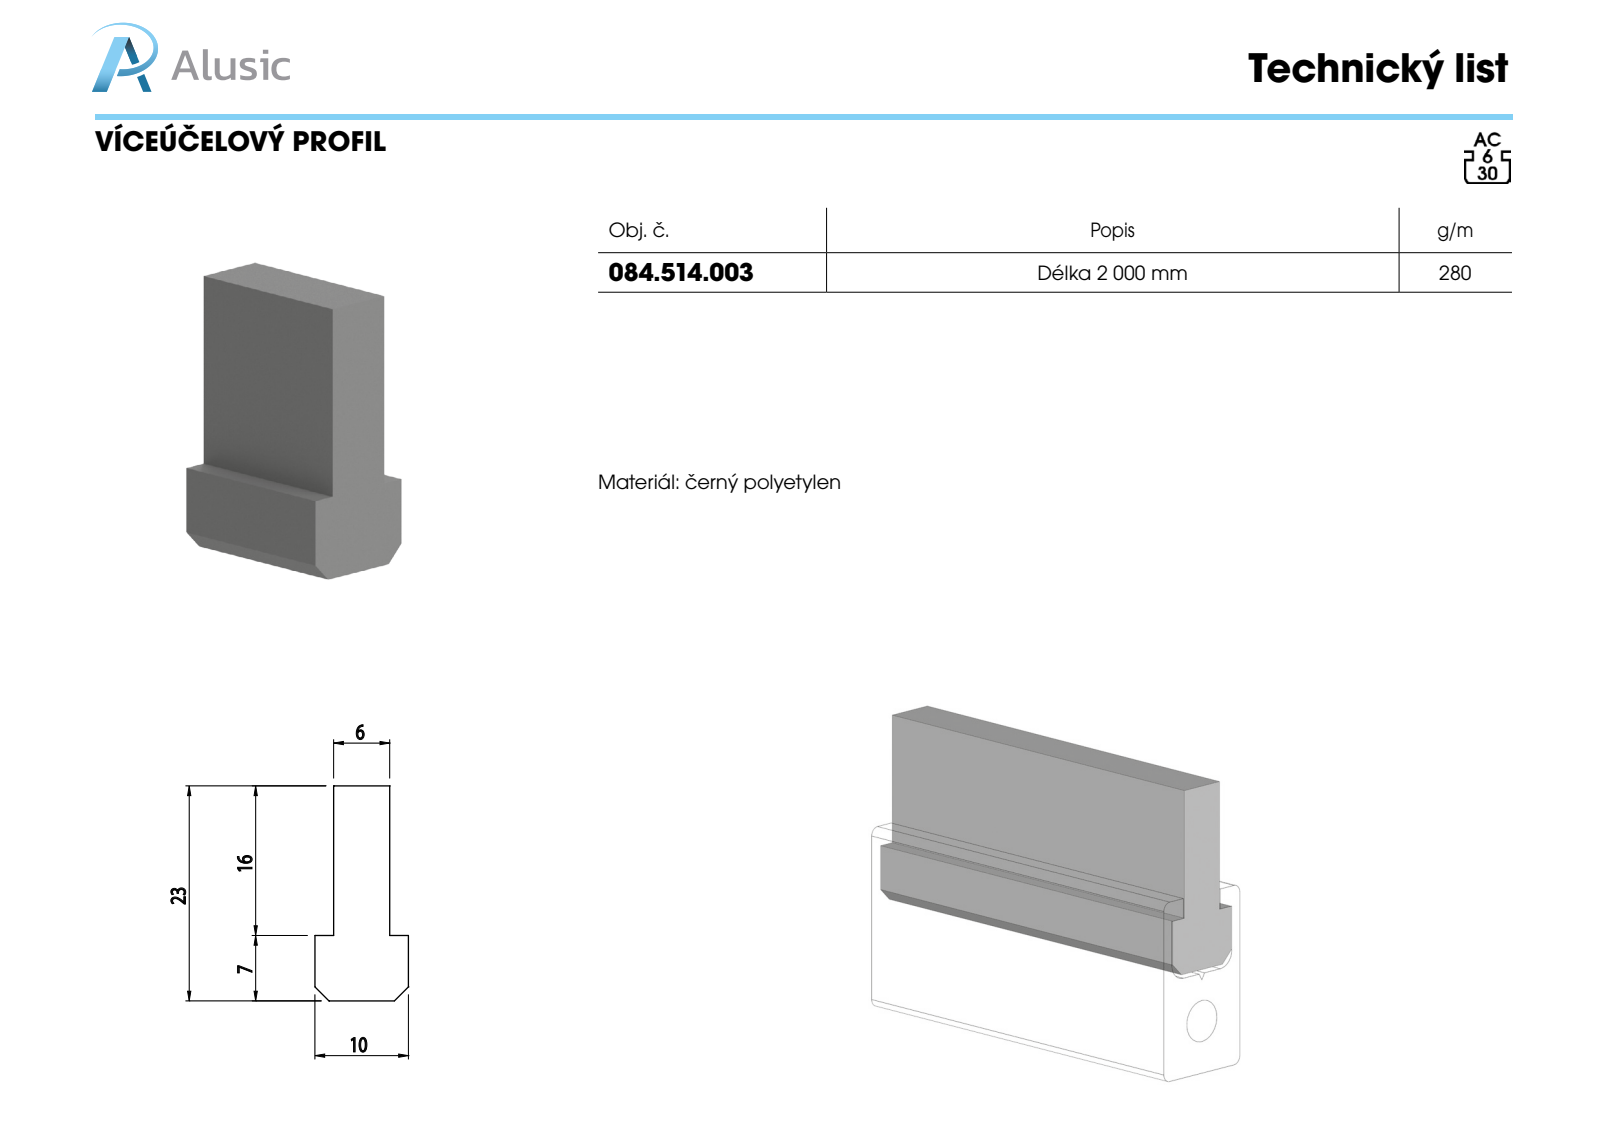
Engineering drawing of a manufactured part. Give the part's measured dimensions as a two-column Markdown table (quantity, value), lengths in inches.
| quantity | value |
| --- | --- |
| part name | 084.514.003 |
| STEP written by | SolidWorks 2011 (CONFIG_CONTROL_DESIGN) |
| units | inches |
| bodies | 1 solid, 12 faces (12 planar, 0 cylindrical, 0 other) |
| overall size | 3.937 × 0.906 × 0.394 |
| volume | 0.999 in³ |
| surface area | 10.47 in² |
| main face-to-face distances | 0.236, 0.079, 0.315, 0.906, 0.394, 0.276, 0.63, 3.937 |
